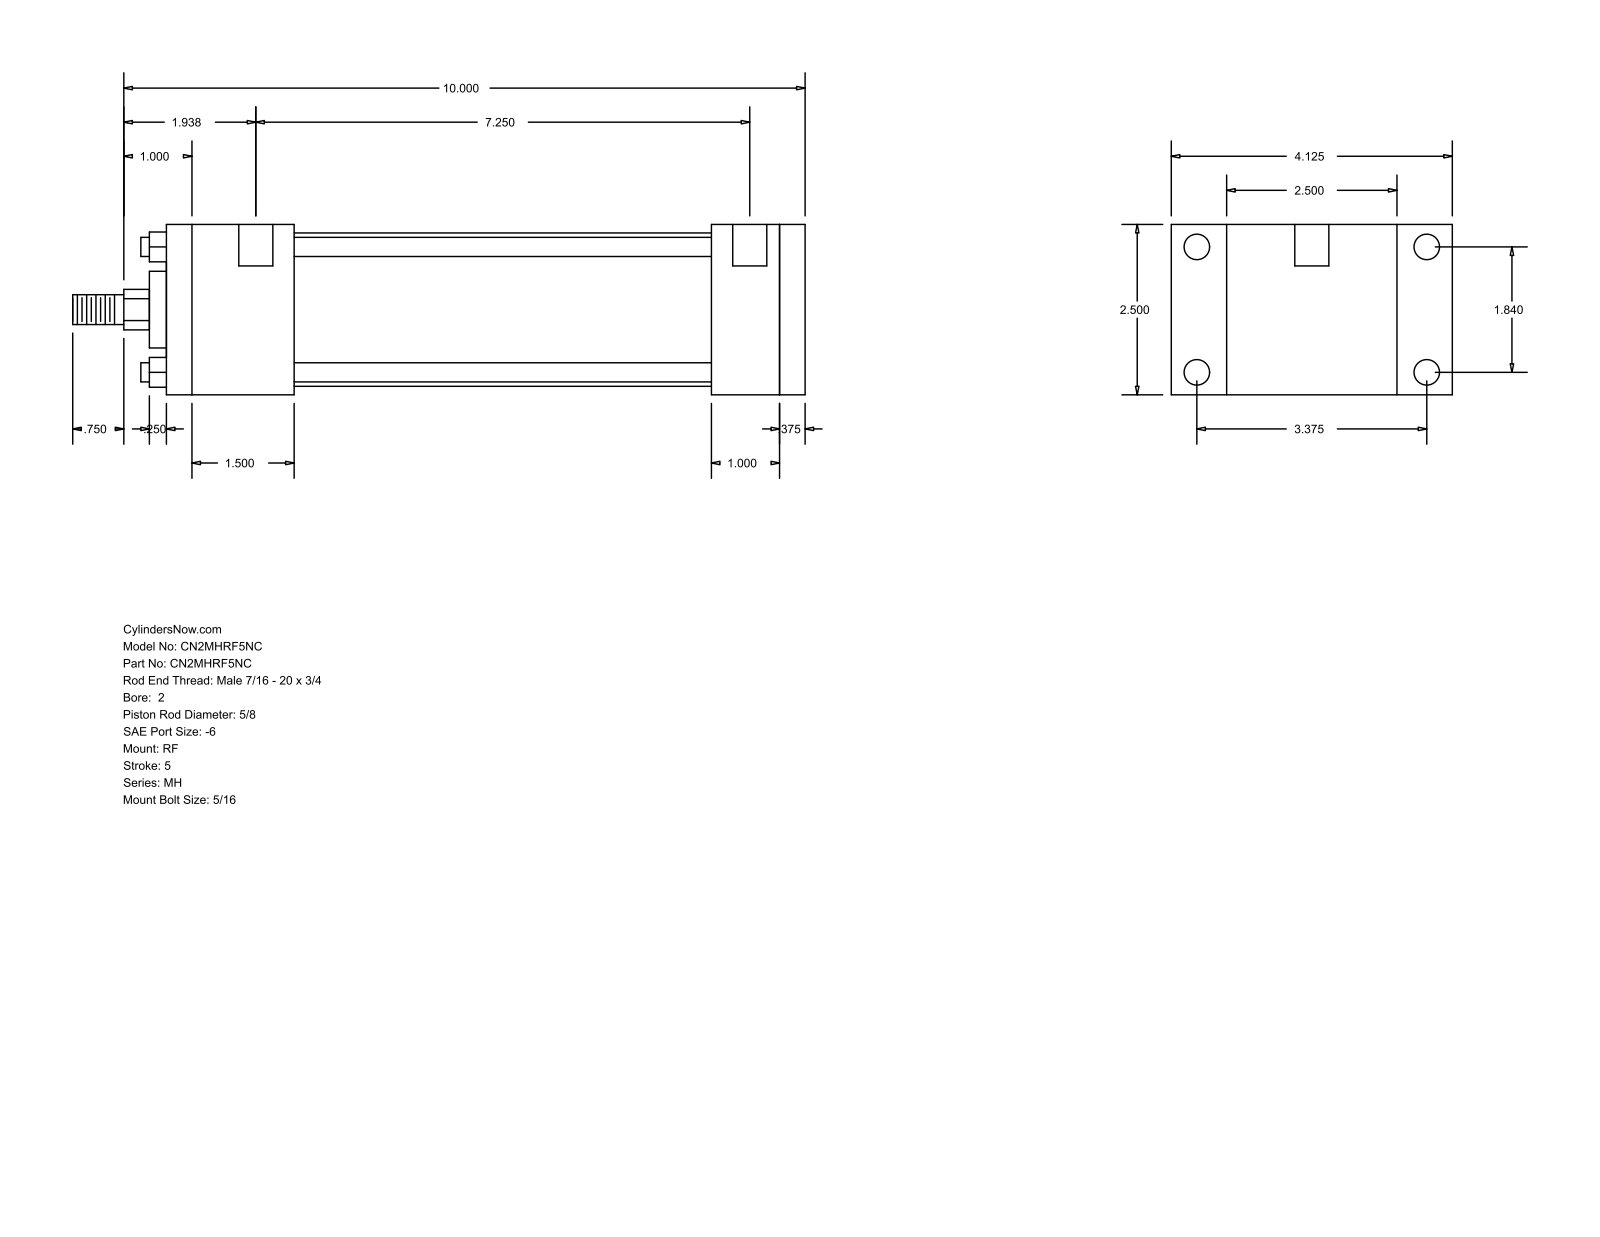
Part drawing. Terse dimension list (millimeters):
name: MH_RF__0200_0.625
written by: GSSL Pune (CONFIG_CONTROL_DESIGN)
unit: mm
bodies: 0 solids, 92 faces (64 planar, 28 cylindrical, 0 other)
size: 273.05 × 104.78 × 63.5
holes: 4× ⌀5.56, 4× ⌀9.53, 2× ⌀12.7
bosses: 4× ⌀7.14, 1× ⌀57.15, 1× ⌀28.57, 1× ⌀15.88, 1× ⌀11.11
rounds: 1× R7.54
face distances: 63.5, 238.12, 9.53, 228.59, 25.4, 34.93, 47.62, 203.19, 155.57, 180.97
hole spacings: 46.74, 85.72, 97.63, 192.09, 3.18, 4.76, 184.15, 187.33
